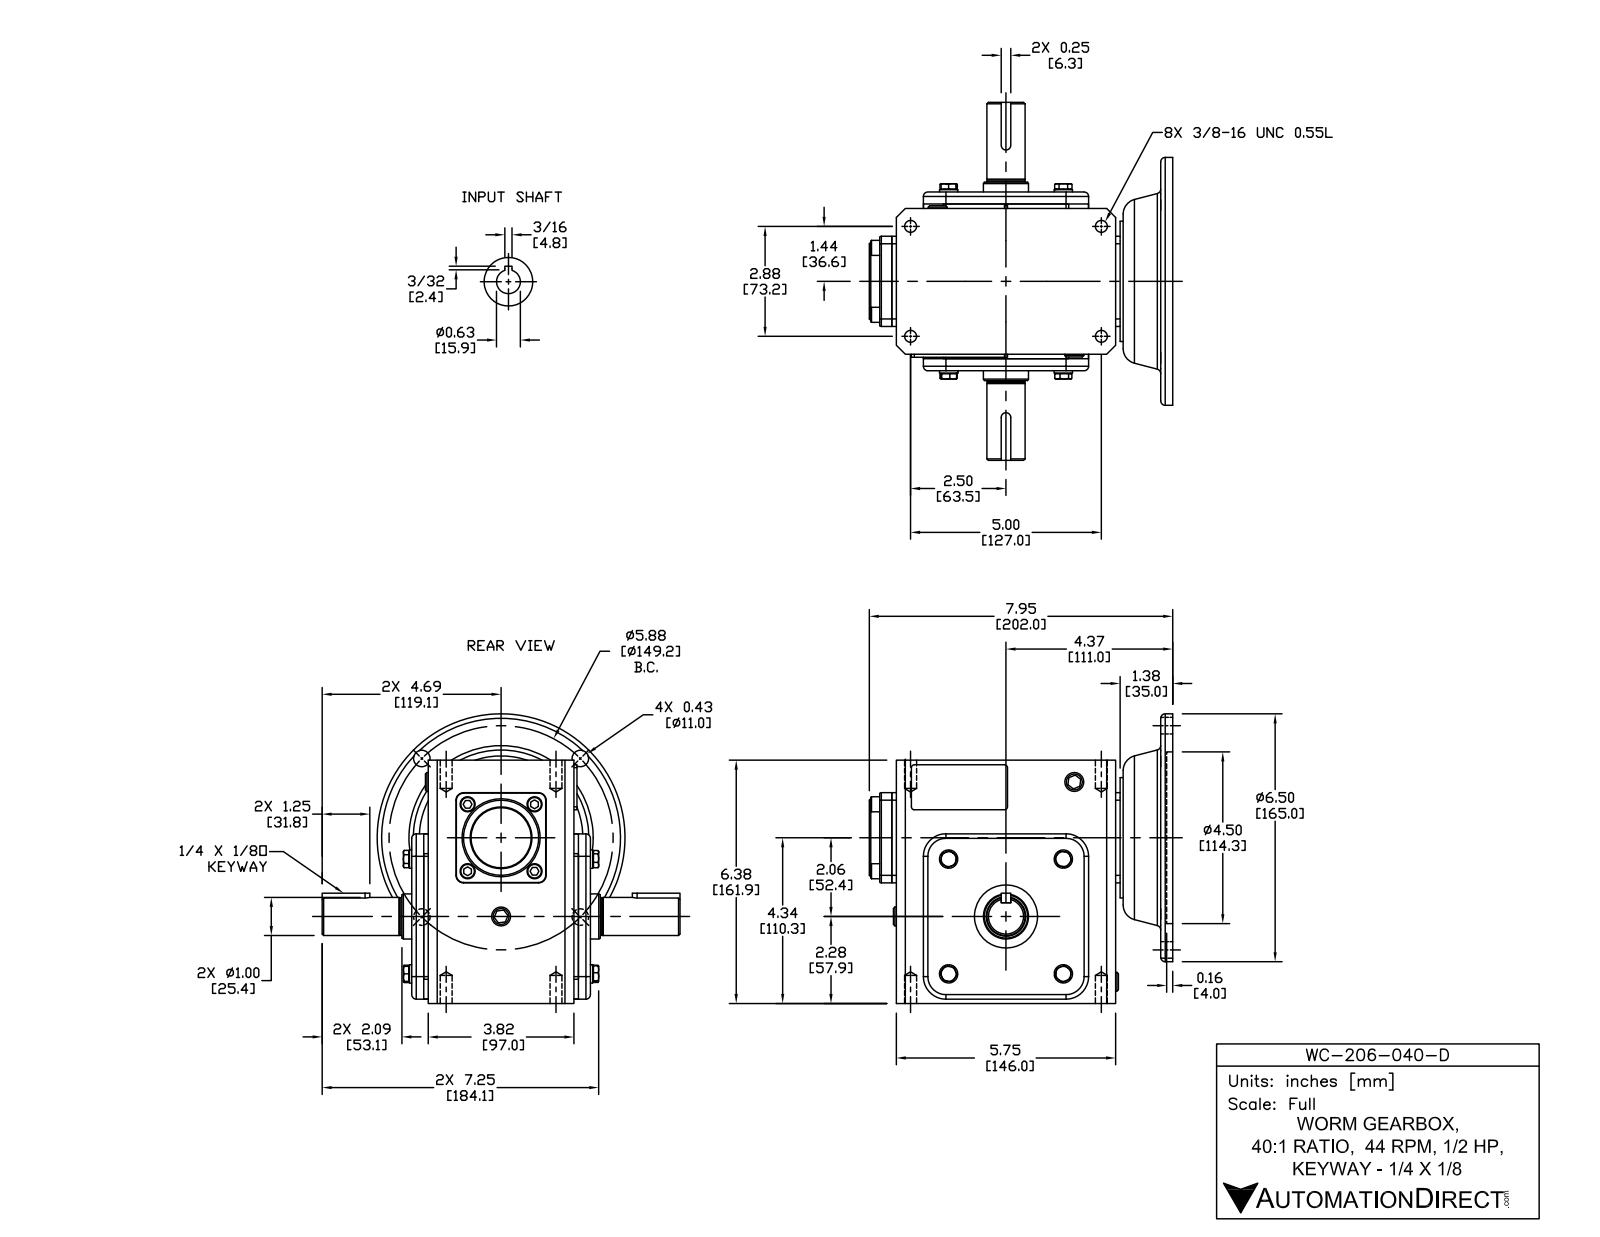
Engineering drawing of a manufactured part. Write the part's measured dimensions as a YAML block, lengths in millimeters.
part_name: "WG-206-040-D"
step_written_by: "SolidWorks 2015 (CONFIG_CONTROL_DESIGN)"
units: millimeters
bodies: {solids: 45, faces: 639, planar: 311, cylindrical: 194, other: 134}
overall_size: [238.3, 202, 192.8]
volume: 2863000
surface_area: 272800
round_holes:
  - {diameter: 8, count: 4}
  - {diameter: 10.3, count: 4}
  - {diameter: 15, count: 1}
  - {diameter: 15.9, count: 1}
  - {diameter: 30, count: 1}
  - {diameter: 37, count: 1}
  - {diameter: 42, count: 1}
  - {diameter: 90, count: 1}
  - {diameter: 114.3, count: 1}
round_bosses_or_shafts:
  - {diameter: 10, count: 8}
  - {diameter: 12.2, count: 4}
  - {diameter: 165, count: 1}
  - {diameter: 80, count: 1}
  - {diameter: 52, count: 1}
  - {diameter: 40, count: 1}
  - {diameter: 30, count: 1}
  - {diameter: 29, count: 1}
partial_cylinders:
  - {radius: 2, count: 8}
  - {radius: 3, count: 8}
  - {radius: 5, count: 4}
  - {radius: 15, count: 4}
  - {radius: 0.5, count: 2}
  - {radius: 1, count: 2}
  - {radius: 3.2, count: 2}
  - {radius: 69, count: 1}
face_to_face_distances: [8, 3, 103, 11, 111, 108, 100, 161.9, 119, 18]
hole_center_spacings: [74.6, 105.5, 52.8, 73.2, 117.6, 127, 146.6, 149.2]
